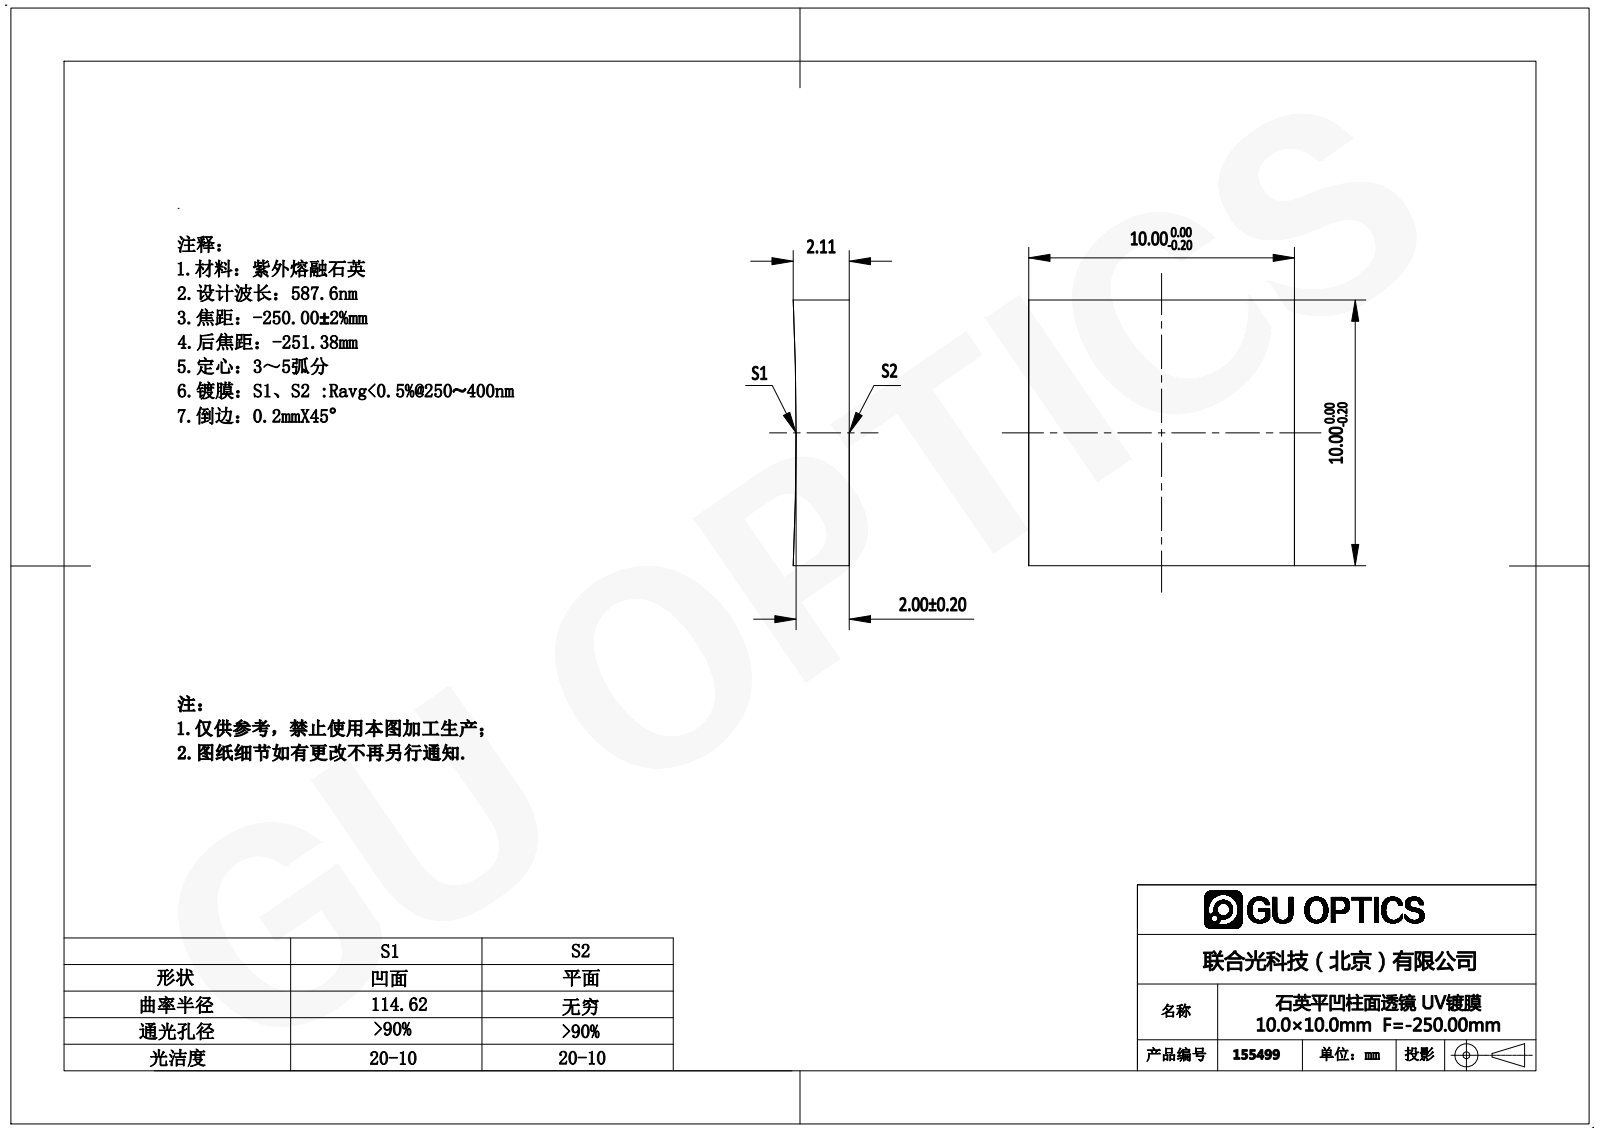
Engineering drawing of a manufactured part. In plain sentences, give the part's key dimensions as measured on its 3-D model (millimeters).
The part is named "155473". Its 3-D file was written by "SolidWorks 2016 (AUTOMOTIVE_DESIGN)". It is 1 solid with 6 faces: 5 planar, 1 cylindrical and 0 other. Overall it measures 10 by 10 by 2.11 millimeters. Its volume is 204 cubic millimeters and its surface area 283 square millimeters. Partial cylindrical surfaces (rounded edges, fillets, slot ends): 1 of radius 114.62. The main face-to-face distances are 10.
